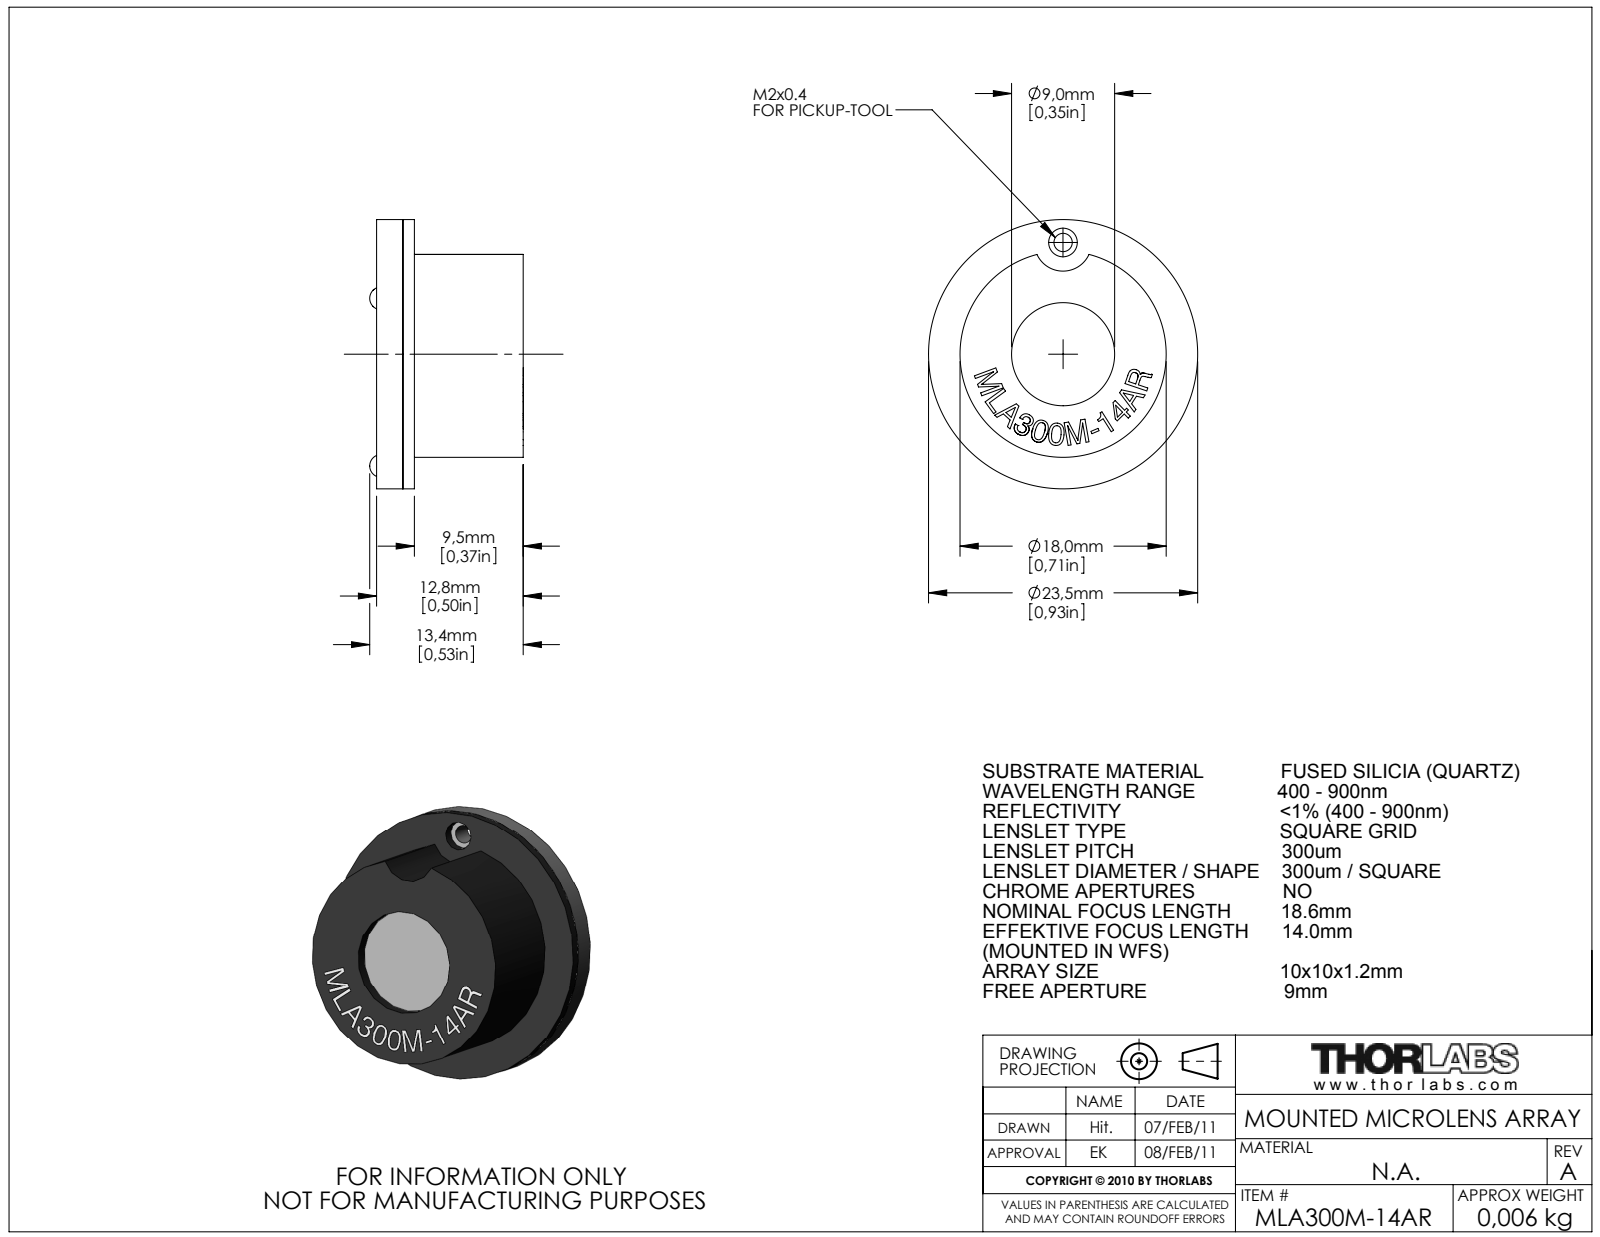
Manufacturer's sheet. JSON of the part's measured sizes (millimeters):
{"part_name": "20679-E0W", "step_written_by": "SolidWorks 2009 (CONFIG_CONTROL_DESIGN)", "units": "millimeters", "bodies": {"solids": 0, "faces": 186, "planar": 100, "cylindrical": 54, "other": 32}, "overall_size": [23.5, 23.5, 13.41], "round_holes": [[3.2, 6], [1.9, 3], [1.5, 1], [1.6, 1], [2.5, 1], [9, 1], [15.5, 1]], "round_bosses_or_shafts": [[3, 6], [23.5, 1], [18, 1]], "partial_cylinders_radius": [[1.5, 4], [2.5, 1]], "face_to_face_distances": [1, 2.3, 3.3, 12.8, 10.5, 9.5, 10.2, 1.2, 11.5, 1.18], "hole_center_spacings": [9.75, 13.79, 9.74, 18.83, 5.05, 16.89, 19.5, 16.88]}
